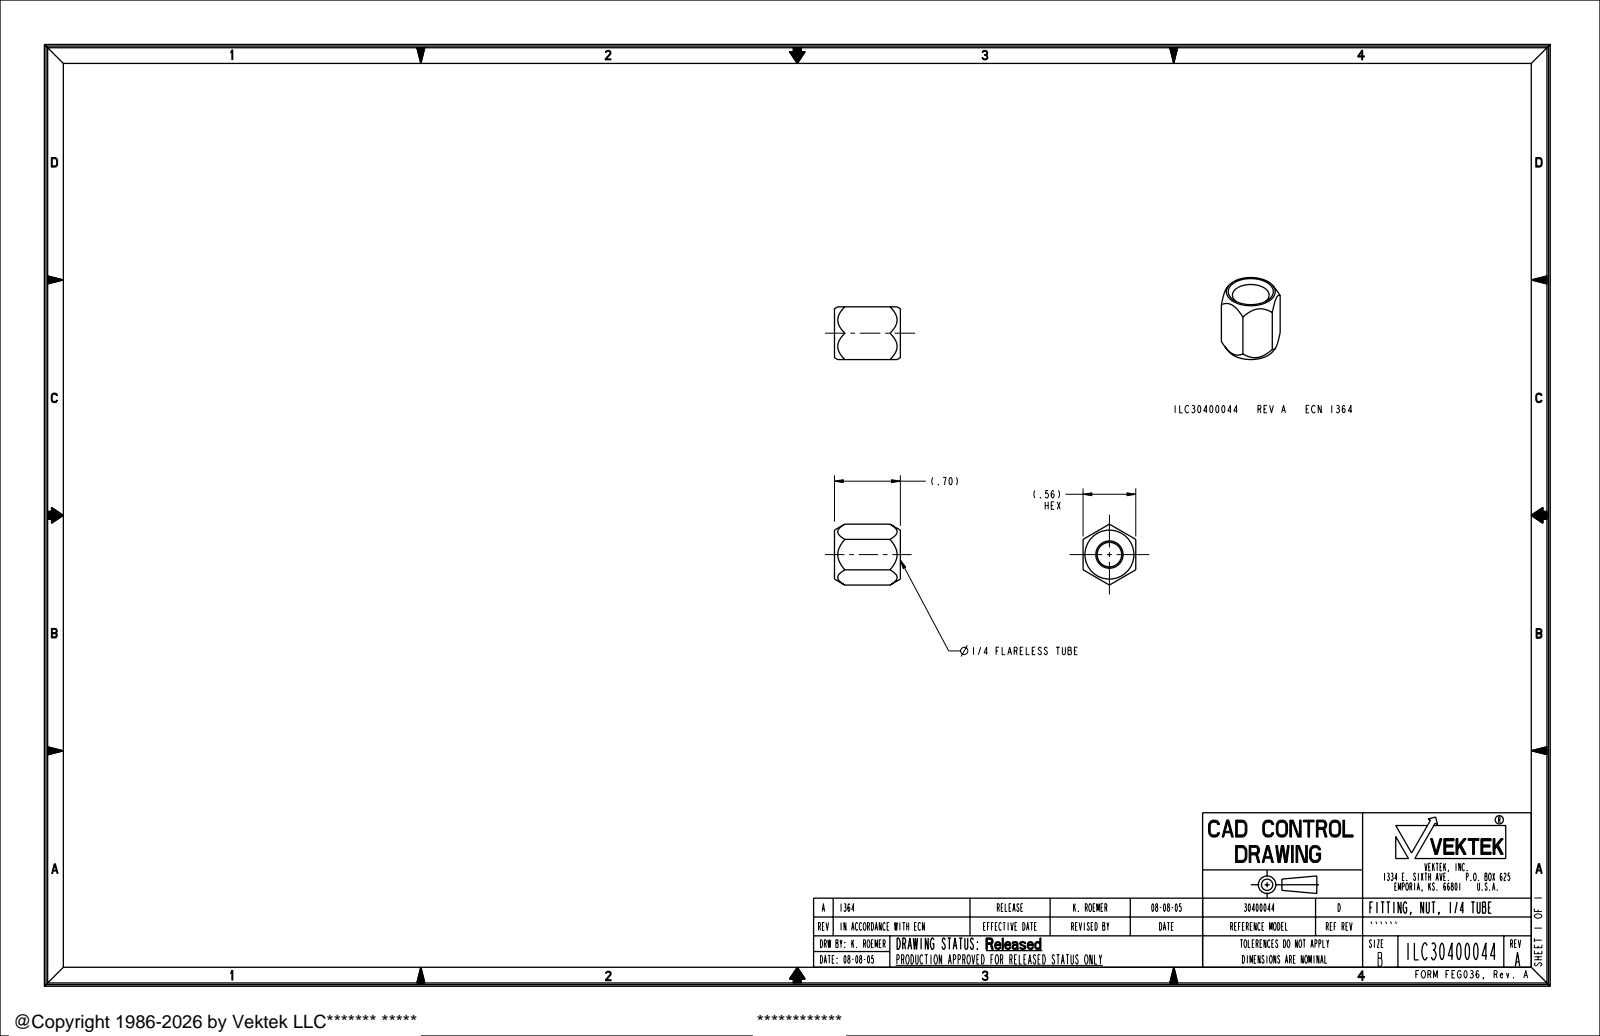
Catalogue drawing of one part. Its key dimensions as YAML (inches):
part_name: "ILC30400044"
step_written_by: "PRO/ENGINEER BY PARAMETRIC TECHNOLOGY CORPORATION, 2004290 (AUTOMOTIVE_DESIGN_CC2)"
units: inches
bodies: {solids: 1, faces: 21, planar: 9, cylindrical: 4, other: 8}
overall_size: [0.7, 0.647, 0.56]
volume: 0.109
surface_area: 2.451
round_holes:
  - {diameter: 0.26, count: 1}
  - {diameter: 0.39, count: 1}
face_to_face_distances: [0.56, 0.12, 0.7, 0.58]
